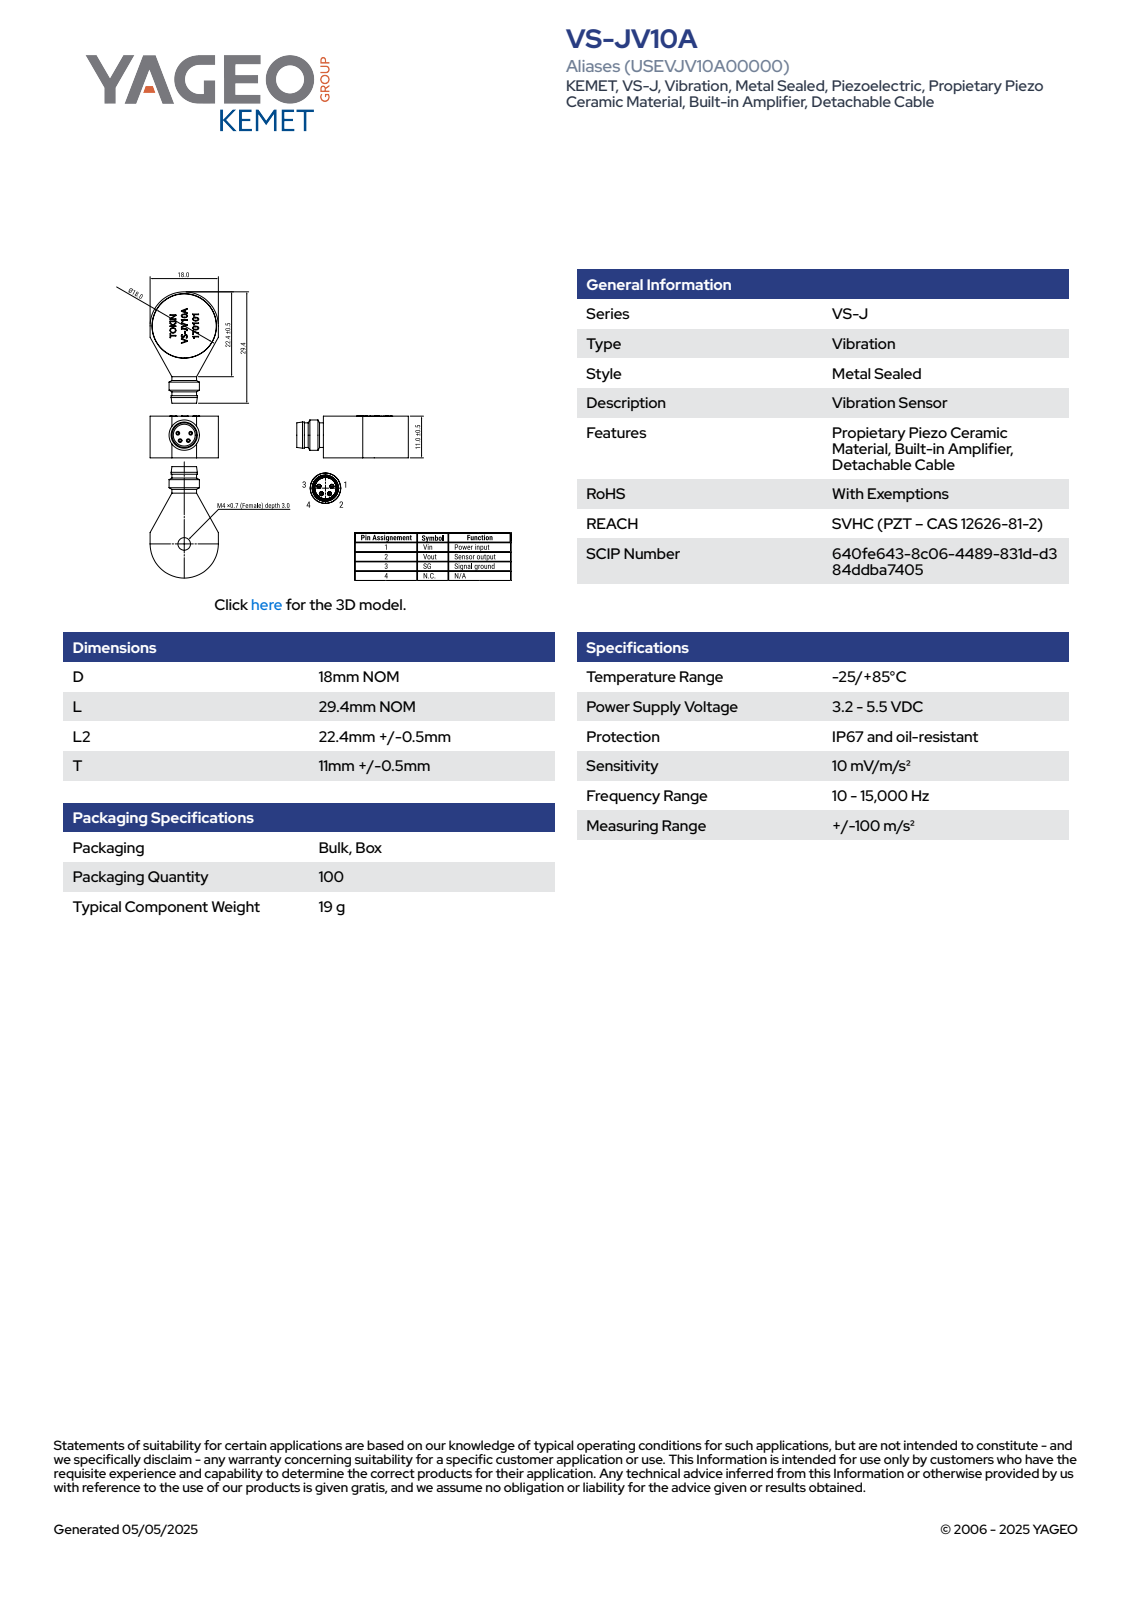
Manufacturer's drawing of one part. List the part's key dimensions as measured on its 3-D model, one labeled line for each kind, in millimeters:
Part name (STEP PRODUCT): SV_KVSJ_L29.4T11.5D18L222.9
STEP written by: SolidWorks 2014 (AUTOMOTIVE_DESIGN)
Units: millimetres
Bodies: 1 solid, 124 faces (73 planar, 39 cylindrical, 12 other)
Overall size (bounding box): 29.4 × 18 × 11.51
Volume: 3 973 mm³ · Surface area: 1 714 mm²
Round holes (diameter × count): ⌀6.96 ×1, ⌀16.72 ×1
Round bosses / shafts (diameter × count): ⌀0.8 ×4, ⌀15.72 ×1, ⌀9.25 ×1, ⌀8.72 ×1, ⌀7.9 ×1
Partial cylindrical surfaces — rounded edges, fillets, slot ends (radius × count): R0.25 ×12, R9 ×1
Main face-to-face distances: 11.5, 11.25, 4.5, 18, 11, 2, 6.5, 2.2, 4.3, 21.64
